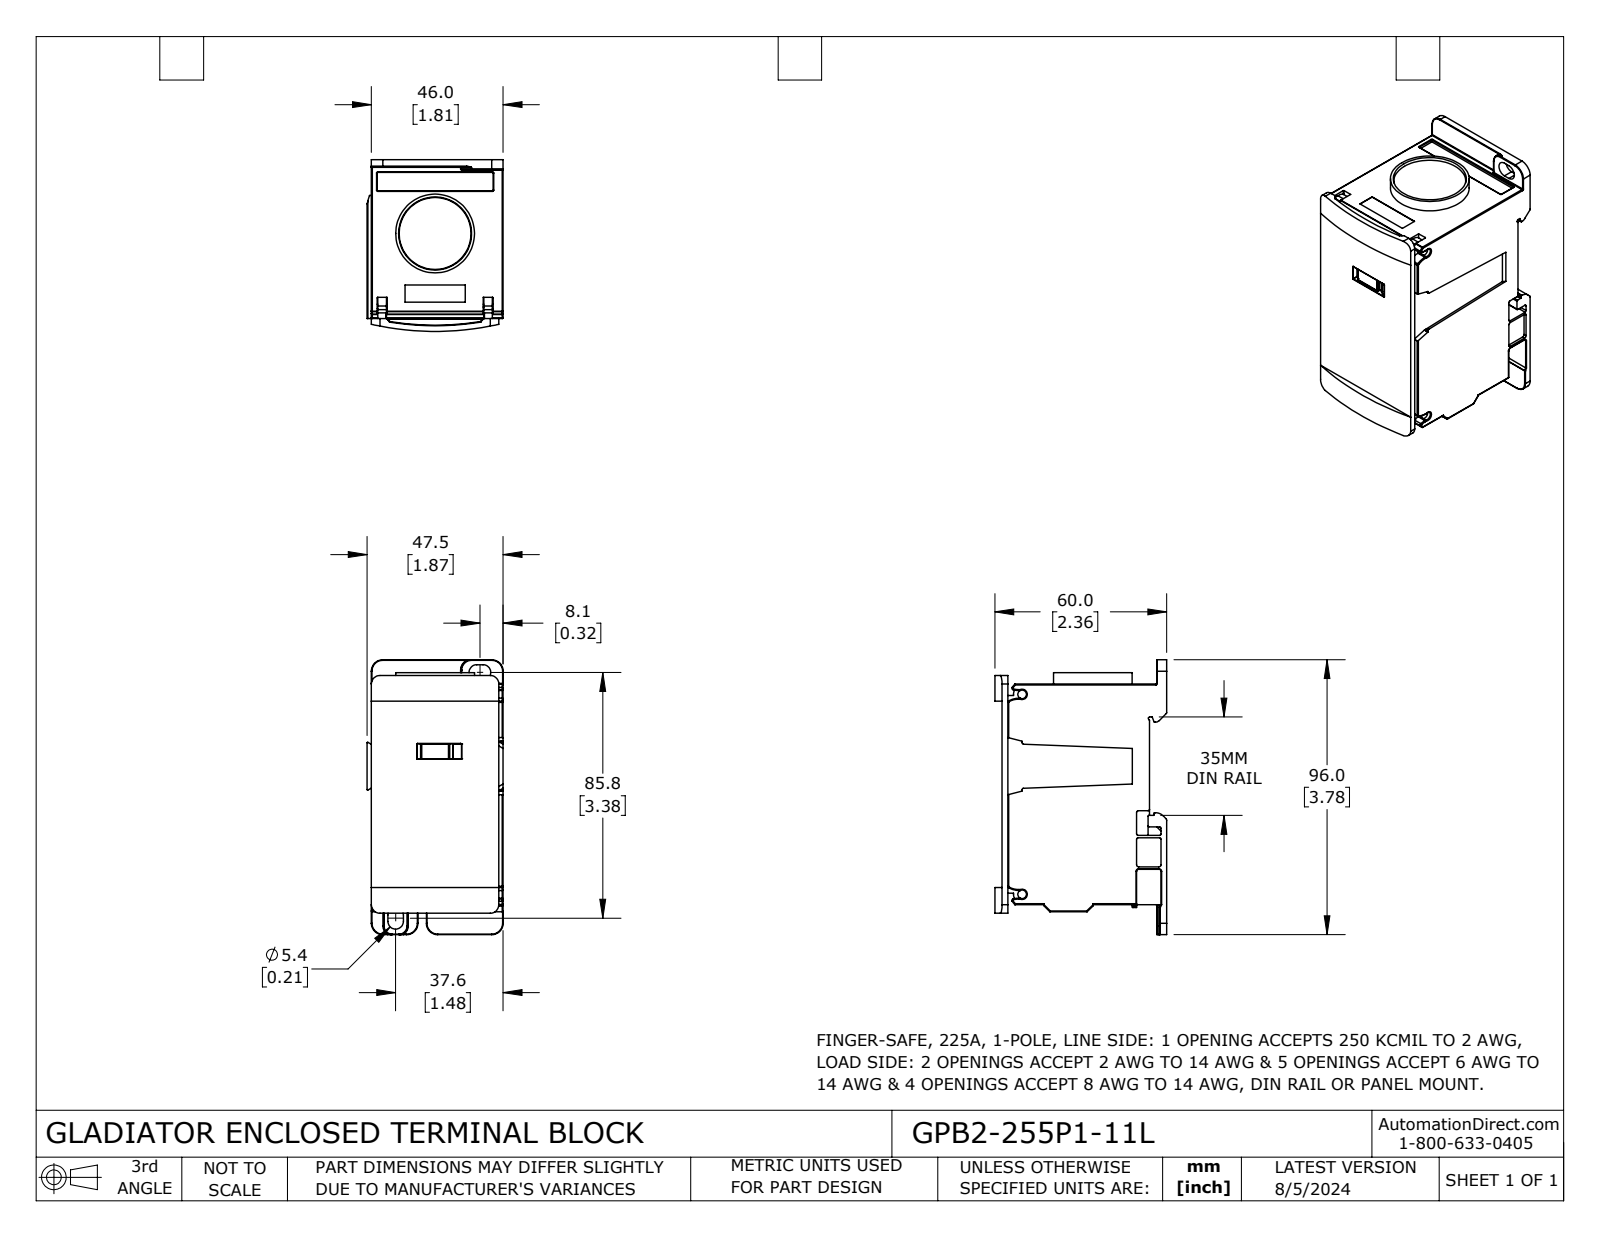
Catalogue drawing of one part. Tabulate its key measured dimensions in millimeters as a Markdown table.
| quantity | value |
| --- | --- |
| part name | GPB2-255P1-11L |
| STEP written by | SolidWorks 2023 (CONFIG_CONTROL_DESIGN) |
| units | millimeters |
| bodies | 1 solid, 626 faces (212 planar, 290 cylindrical, 124 other) |
| overall size | 96.2 × 60 × 47.5 |
| volume | 189 900 mm³ |
| surface area | 29 200 mm² |
| round holes (diameter × count) | 10 × 5, 8.5 × 4, 3 × 2, 12 × 2 |
| round bosses / shafts (diameter × count) | 27.5 × 1 |
| partial cylindrical surfaces (radius × count) | 0.2 × 74, 0.1 × 25, 0.3 × 24, 0.5 × 16, 4 × 9, 3 × 8, 0.8 × 6, 2.7 × 4 |
| main face-to-face distances | 46, 57.5, 1, 6, 51.5, 2, 4, 76, 77, 3 |
| hole center spacings | 9.5, 10.5, 14.1, 21.5, 23.5, 11, 11.5, 12.3 |
